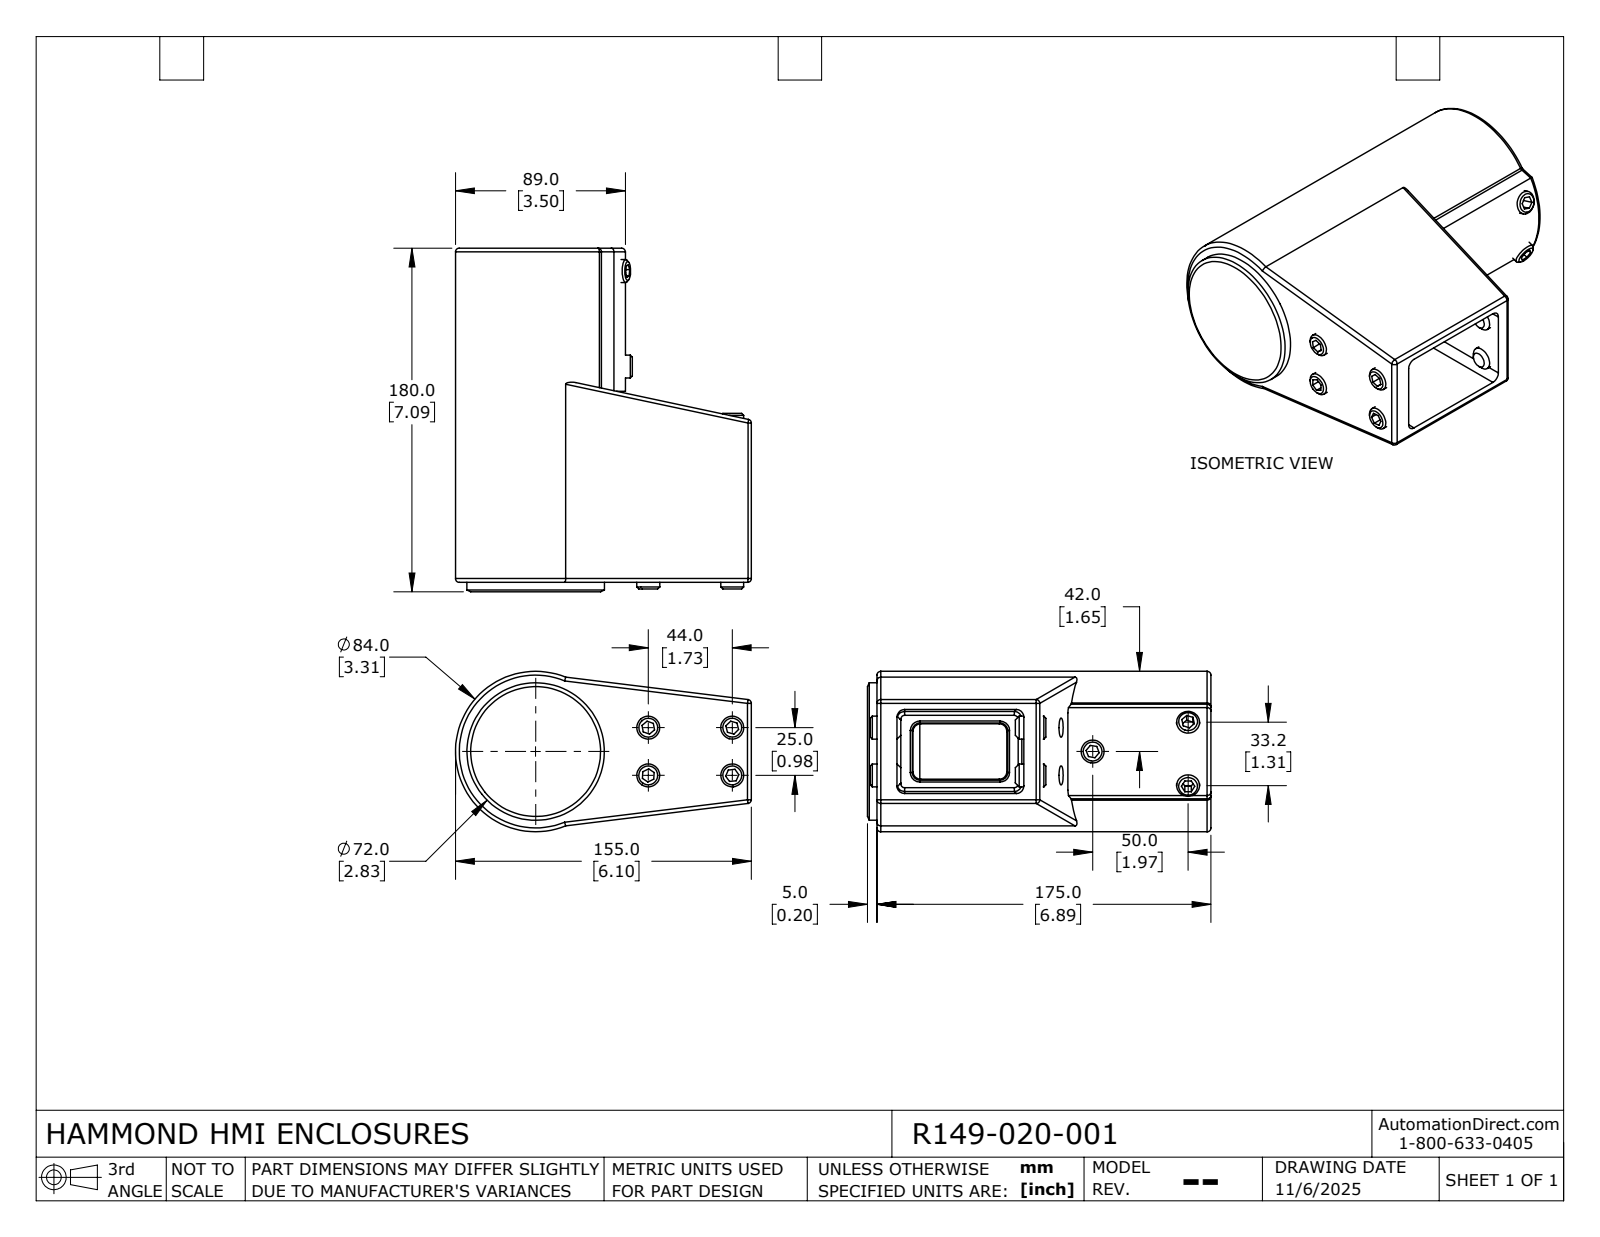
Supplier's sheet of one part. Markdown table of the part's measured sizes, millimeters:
| quantity | value |
| --- | --- |
| part name | R149-020-001 |
| STEP written by | SolidWorks 2024 (AUTOMOTIVE_DESIGN) |
| units | millimeters |
| bodies | 15 solids, 321 faces (182 planar, 68 cylindrical, 71 other) |
| overall size | 354 × 343 × 84 |
| volume | 931 820 mm³ |
| surface area | 354 532 mm² |
| round holes (diameter × count) | 10.11 × 7, 64 × 1 |
| round bosses / shafts (diameter × count) | 12 × 7, 72 × 1, 70 × 1, 66 × 1 |
| partial cylindrical surfaces (radius × count) | 2 × 20, 4 × 12, 1 × 4, 42 × 1, 47 × 1 |
| main face-to-face distances | 3, 37, 57, 40, 34, 15.5, 72.5, 60, 54, 69.5 |
| hole center spacings | 25, 44, 50.61, 60.31, 103.76 |
